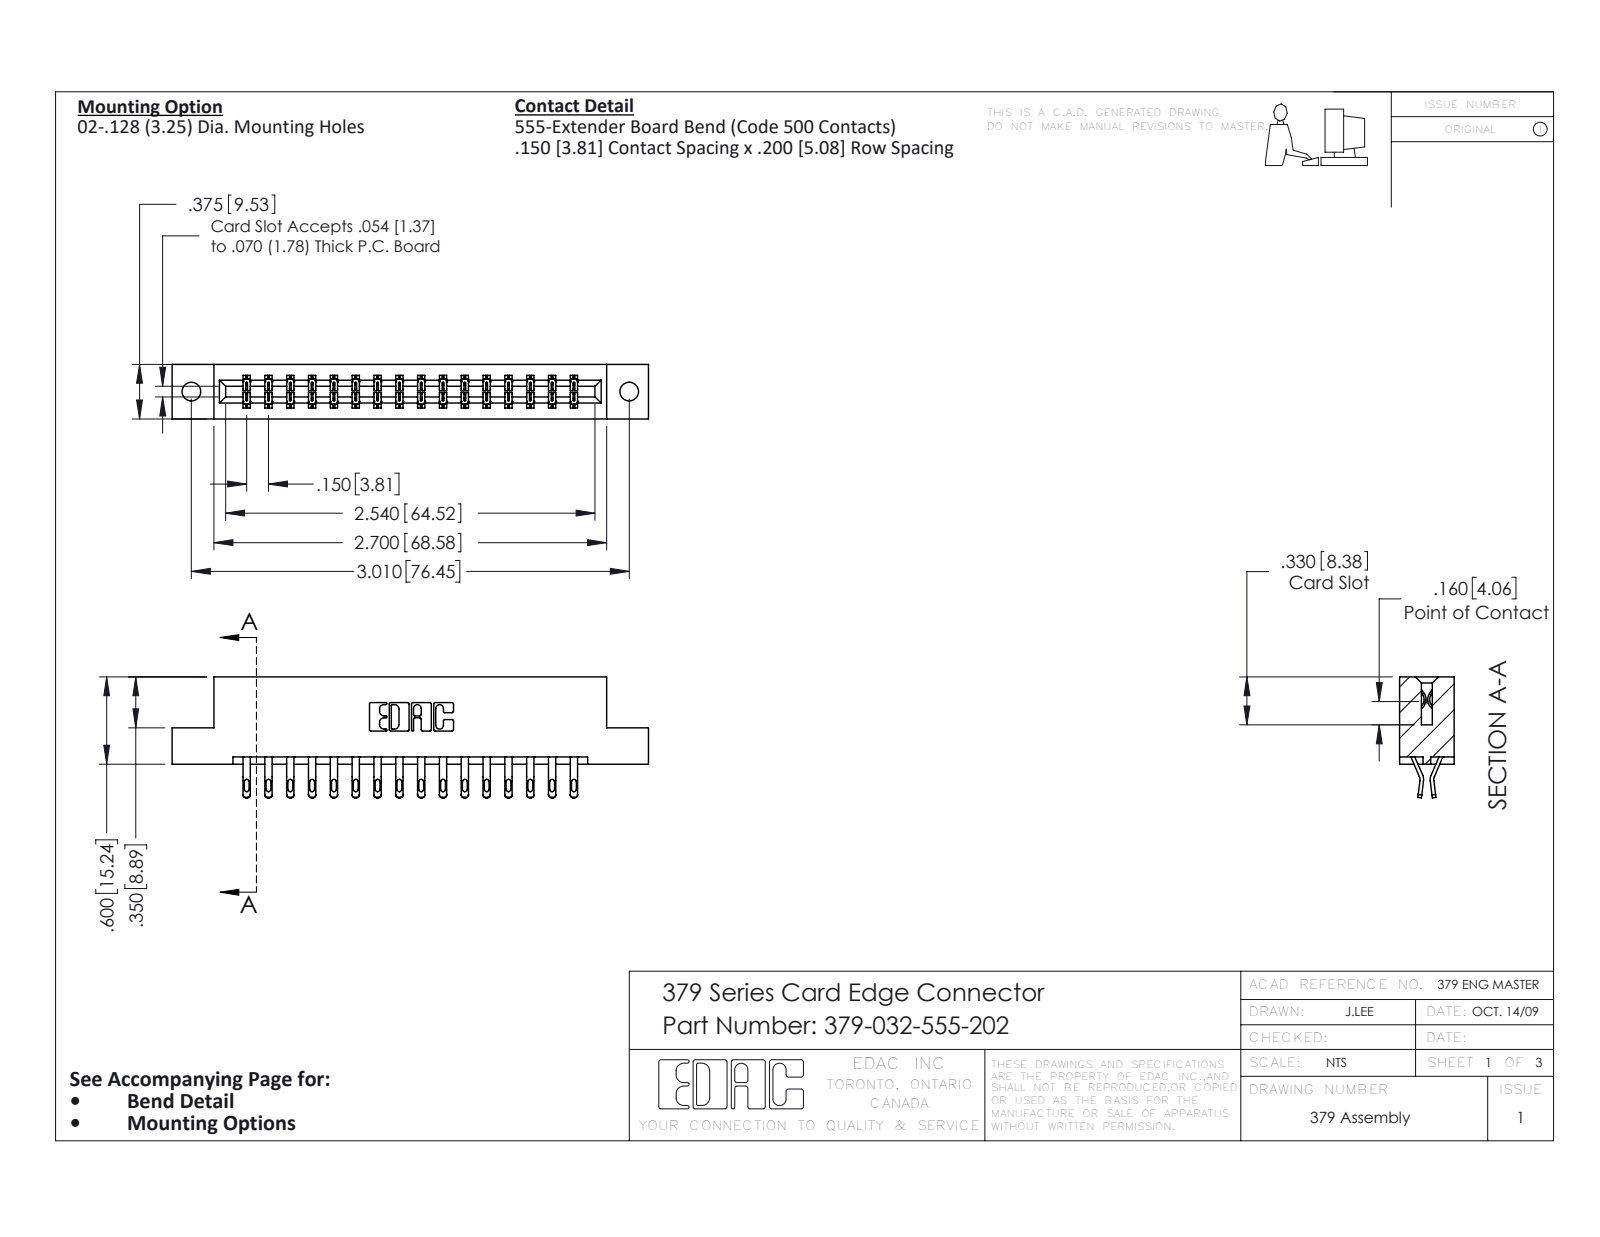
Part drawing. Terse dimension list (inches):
name: 379 Part_Flush - .128 Dia; 345-292-001_555 Tail; 379-032-555-202
written by: SolidWorks 2020 (CONFIG_CONTROL_DESIGN)
unit: in
bodies: 33 solids, 1970 faces (1158 planar, 812 cylindrical, 0 other)
size: 3.275 × 0.832 × 0.375
volume: 0.524 in³; area: 14.71 in²
holes: 2× ⌀0.128
rounds: 64× R0.016, 64× R0.02, 48× R0.006, 22× R0.01, 6× R0.007, 6× R0.031, 3× R0.026, 2× R0.01
face distances: 0.3, 0.375, 0.075, 0.2, 0.15, 0.1, 0.05, 0.6, 0.55, 0.225
hole spacings: 3.01
